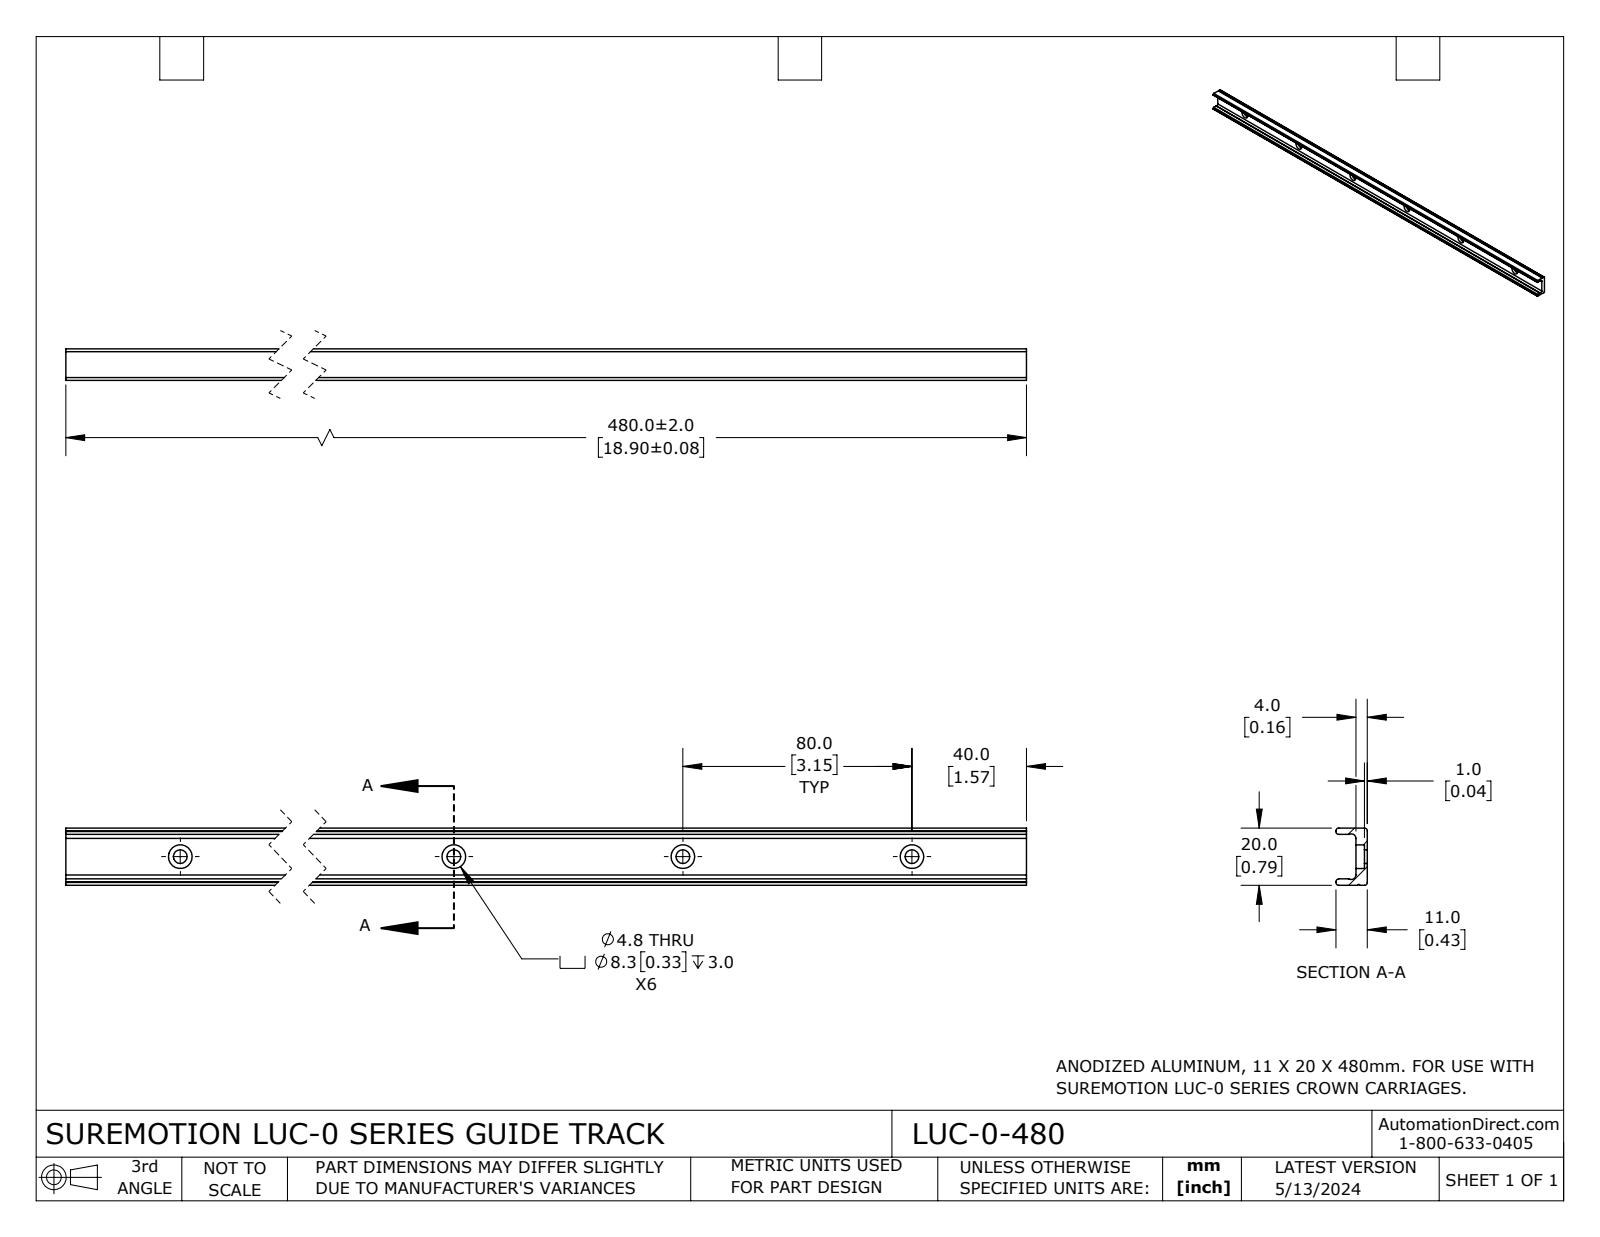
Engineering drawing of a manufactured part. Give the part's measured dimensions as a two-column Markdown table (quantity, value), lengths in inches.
| quantity | value |
| --- | --- |
| part name | LUC-0-480 |
| STEP written by | SolidWorks 2023 (CONFIG_CONTROL_DESIGN) |
| units | inches |
| bodies | 1 solid, 52 faces (17 planar, 35 cylindrical, 0 other) |
| overall size | 18.898 × 0.787 × 0.433 |
| volume | 3.159 in³ |
| surface area | 55.07 in² |
| round holes (diameter × count) | 0.189 × 6, 0.325 × 5, 0.325 × 1 |
| partial cylindrical surfaces (radius × count) | 0.039 × 8, 0.063 × 2, 0.013 × 1 |
| main face-to-face distances | 0.158, 0.787, 0.088, 0.7, 0.612, 0.433, 0.275, 0.04, 0.118, 0.393 |
| hole center spacings | 3.15, 6.299, 9.449, 12.598, 15.748 |
